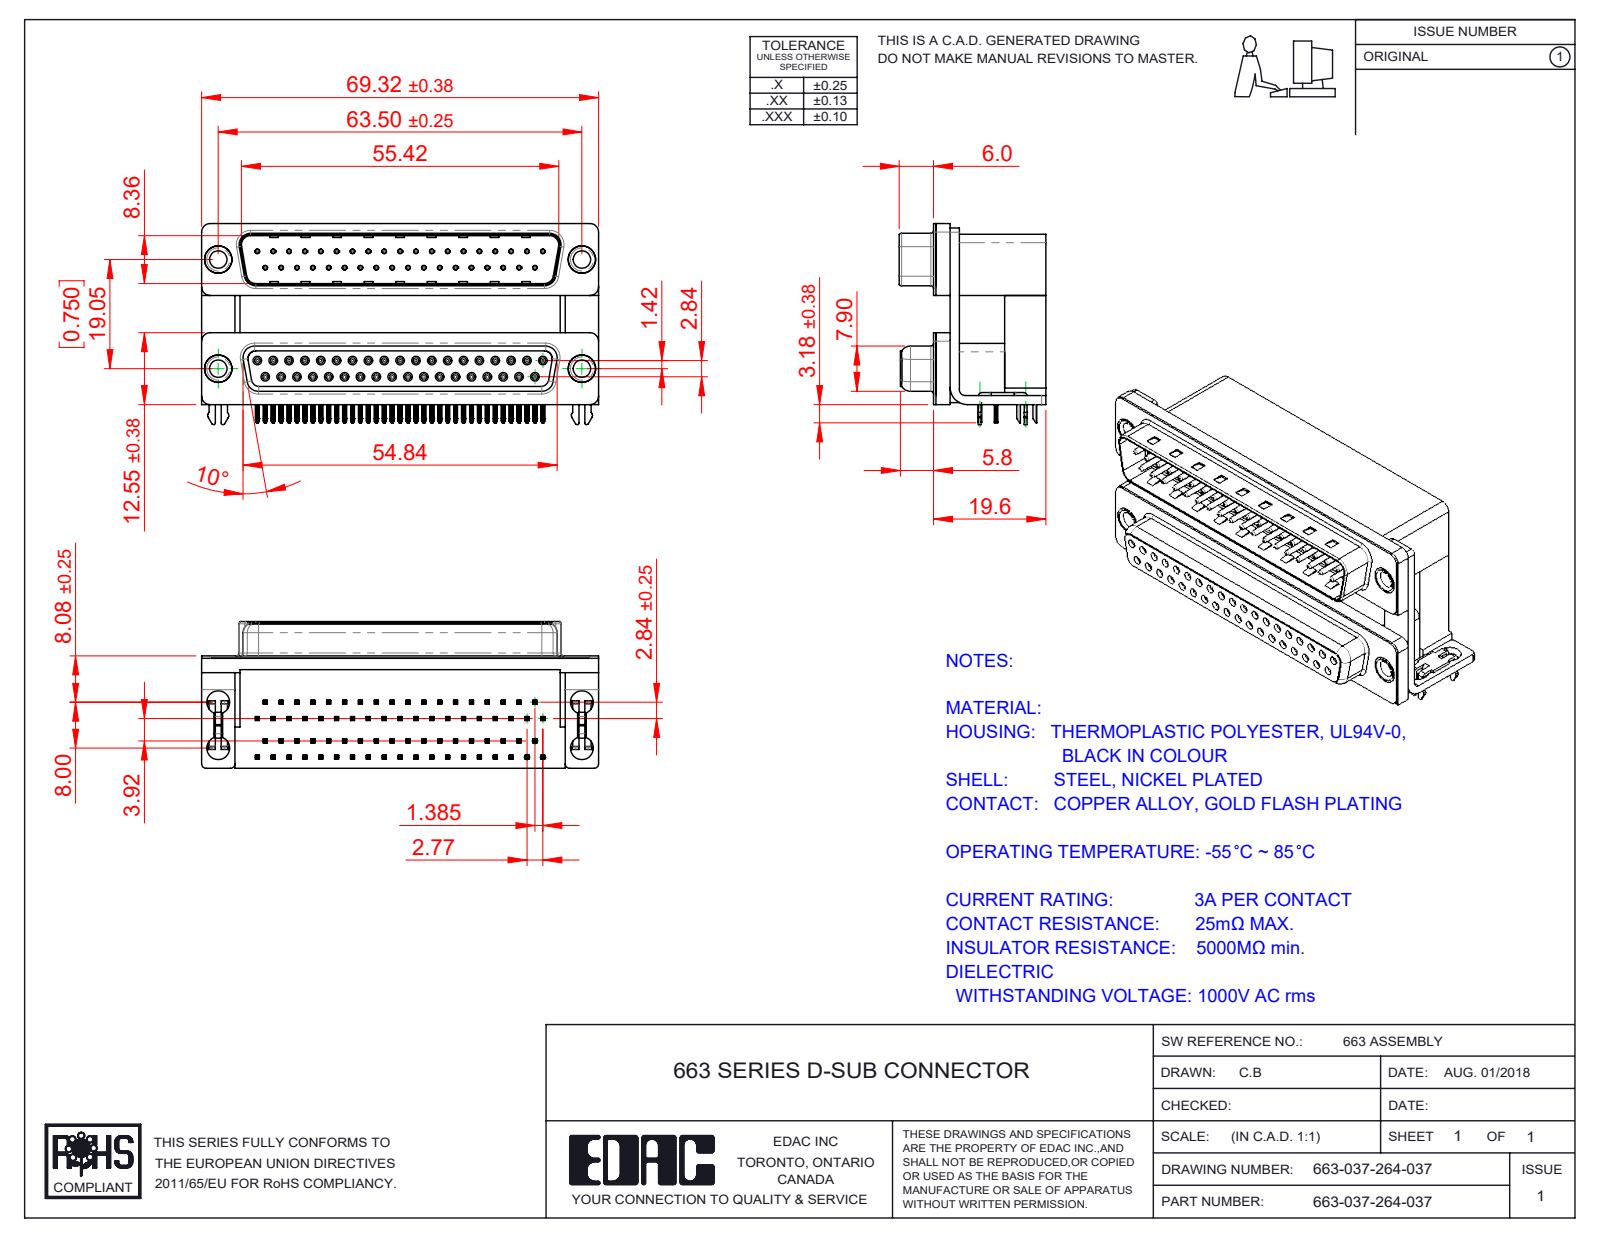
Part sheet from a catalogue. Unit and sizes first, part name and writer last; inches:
Units: inches
Overall size (bounding box): 2.729 × 1.382 × 1.008
Round holes (diameter × count): ⌀0.031 ×74, ⌀0.014 ×37, ⌀0.035 ×37, ⌀0.157 ×8, ⌀0.12 ×4, ⌀0.138 ×4, ⌀0.189 ×4, ⌀0.197 ×4
Round bosses / shafts (diameter × count): ⌀0.047 ×37, ⌀0.03 ×37, ⌀0.193 ×4, ⌀0.187 ×4, ⌀0.152 ×4
Partial cylindrical surfaces — rounded edges, fillets, slot ends (radius × count): R0.004 ×298, R0.01 ×158, R0.006 ×148, R0.005 ×74, R0.014 ×74, R0.013 ×37, R0.011 ×18, R0.02 ×16
Main face-to-face distances: 0.756, 0.016, 0.283, 0.472, 0.421, 0.736, 1.157, 0.75, 0.112, 0.657
Hole centre spacings: 0.124, 0.109, 0.218, 0.327, 0.436, 0.545, 0.654, 0.763
Volume: 1.904 in³ · Surface area: 50.52 in²
Bodies: 87 solids, 9013 faces (4843 planar, 2191 cylindrical, 1979 other)
Part name (STEP PRODUCT): 663 Mounting Bracket_2ProngM; 663 Shell Receptacle_37 Contacts; 663 Contact Bottom Upper_M; 663 Housing Upper_37 Contacts M (+8 more)
STEP written by: SolidWorks 2020 (CONFIG_CONTROL_DESIGN)
